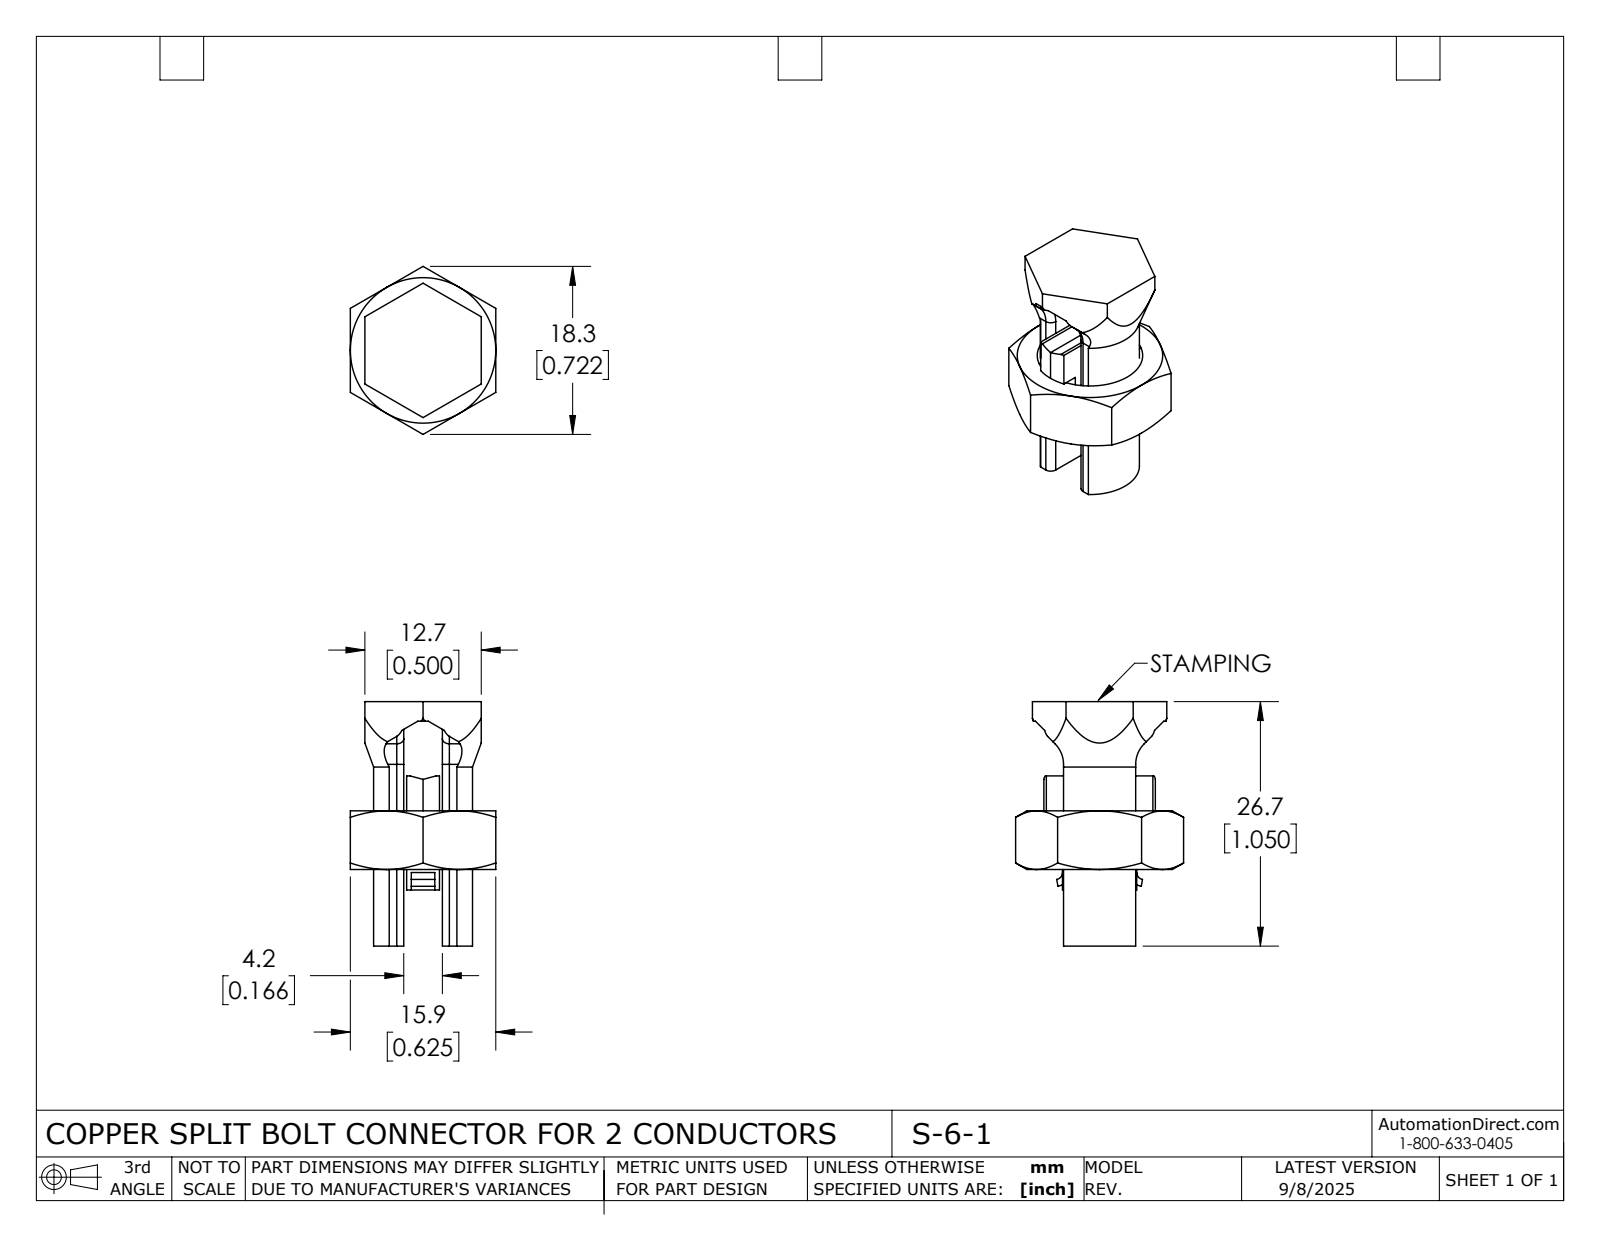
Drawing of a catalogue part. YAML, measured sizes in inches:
part_name: "S-6-1"
step_written_by: "SolidWorks 2024 (AUTOMOTIVE_DESIGN)"
units: inches
bodies: {solids: 3, faces: 101, planar: 53, cylindrical: 23, other: 25}
overall_size: [1.05, 0.722, 0.625]
volume: 0.169
surface_area: 3.925
round_holes:
  - {diameter: 0.388, count: 1}
partial_cylinders:
  - {radius: 0.03, count: 10}
  - {radius: 0.06, count: 2}
  - {radius: 0.125, count: 2}
  - {radius: 0.212, count: 1}
  - {radius: 0.239, count: 1}
face_to_face_distances: [0.013, 0.154, 0.625, 0.166, 0.063, 0.563, 0.141, 0.23, 0.242, 0.383]
